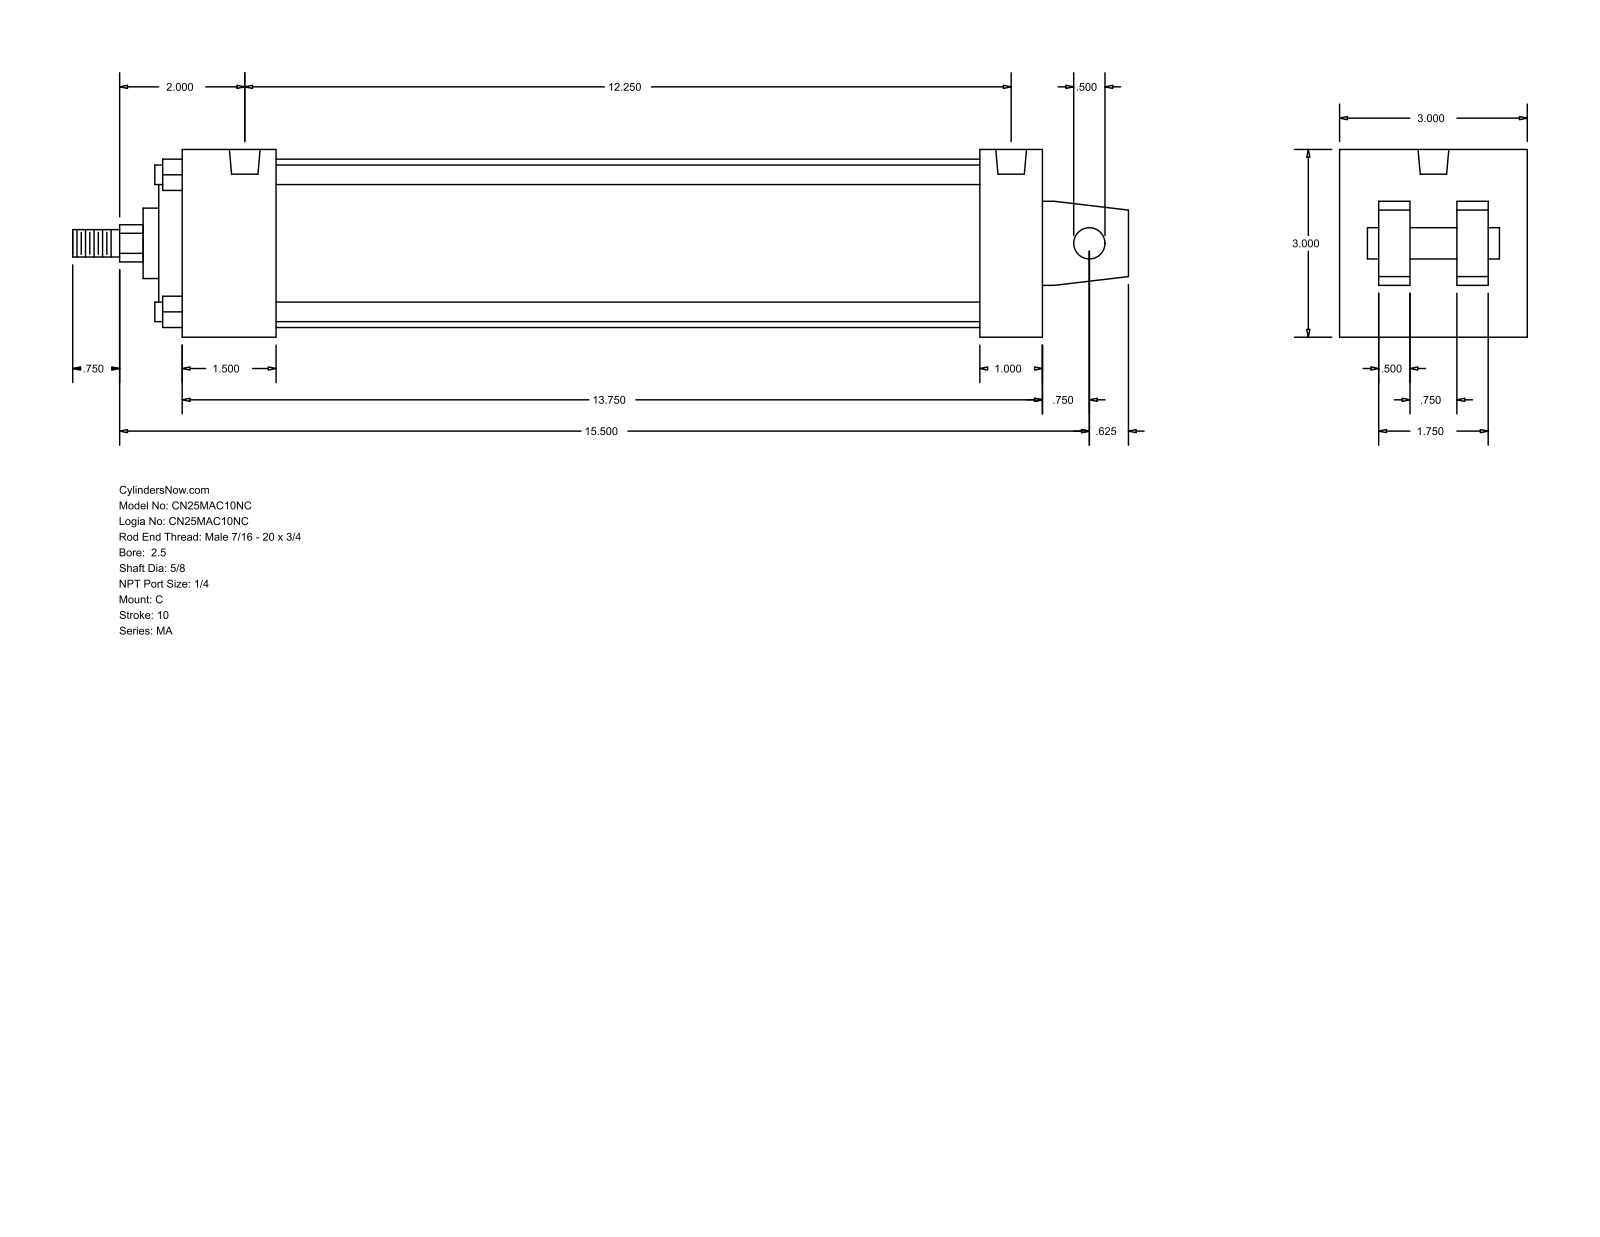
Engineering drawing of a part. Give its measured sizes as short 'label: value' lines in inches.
name: MA_C__0250_0.625
written by: GSSL Pune (CONFIG_CONTROL_DESIGN)
unit: in
bodies: 0 solids, 105 faces (77 planar, 28 cylindrical, 0 other)
size: 16.875 × 3 × 3
holes: 4× ⌀0.313, 2× ⌀0.492
bosses: 4× ⌀0.313, 1× ⌀2.69, 1× ⌀2, 1× ⌀1.125, 1× ⌀0.625, 1× ⌀0.5, 1× ⌀0.437
rounds: 1× R0.297
face distances: 3, 13.75, 0.5, 0.625, 1.875, 1, 1.5, 12.75, 11.25, 12.25
hole spacings: 12.25
